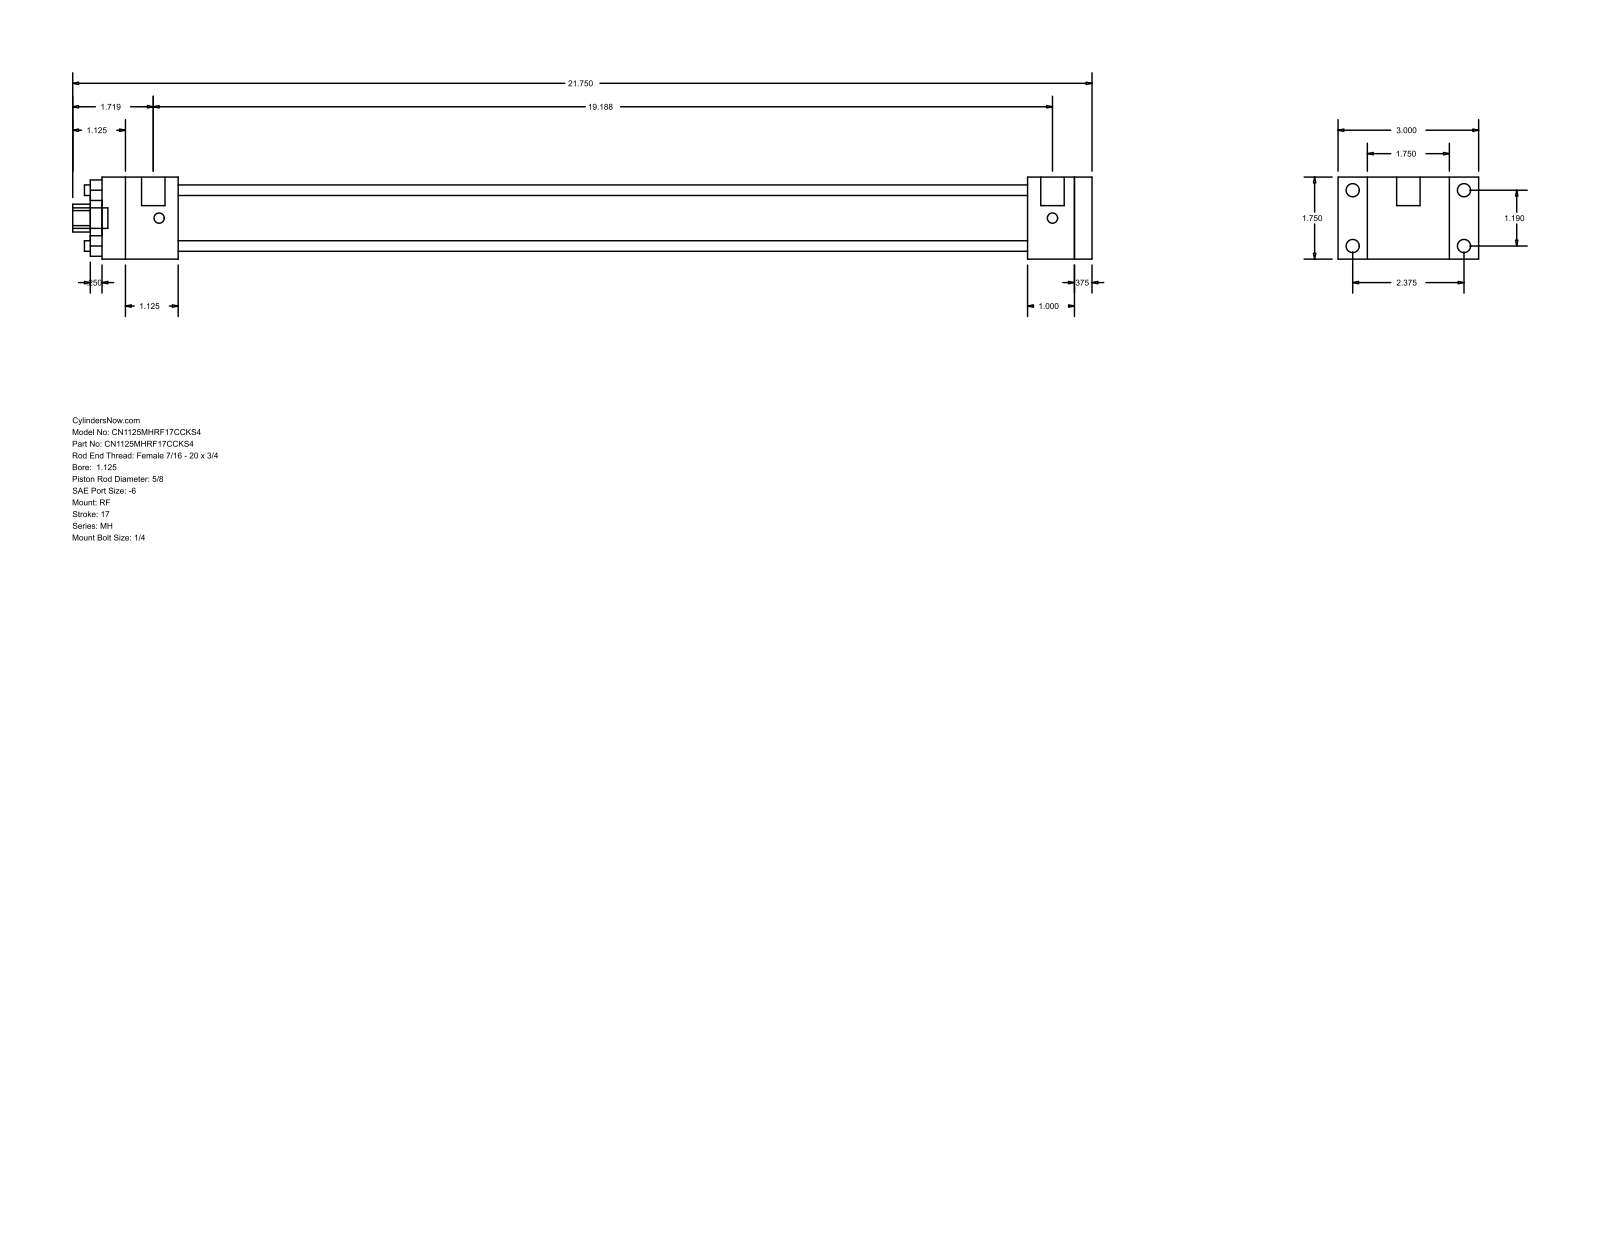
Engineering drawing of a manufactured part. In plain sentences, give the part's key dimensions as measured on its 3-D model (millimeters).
The part is named "MH_RF__0112_0.625". Its 3-D file was written by "GSSL Pune (CONFIG_CONTROL_DESIGN)". It is 0 solids with 92 faces: 64 planar, 28 cylindrical and 0 other. Overall it measures 552.45 by 76.2 by 44.45 millimeters. Round holes: 4 of diameter 5.71, 1 of diameter 15.88, 1 of diameter 28.57, 1 of diameter 34.92. Round bosses or shafts: 4 of diameter 7.14, 4 of diameter 5.56, 2 of diameter 12.7, 1 of diameter 11.11. Partial cylindrical surfaces (rounded edges, fillets, slot ends): 1 of radius 7.54. The main face-to-face distances are 44.46, 9.53, 536.57, 15.87, 485.77, 495.3, 460.37, 25.4, 34.93, 41.27. The hole center spacings are 21.37, 30.22, 42.74.
